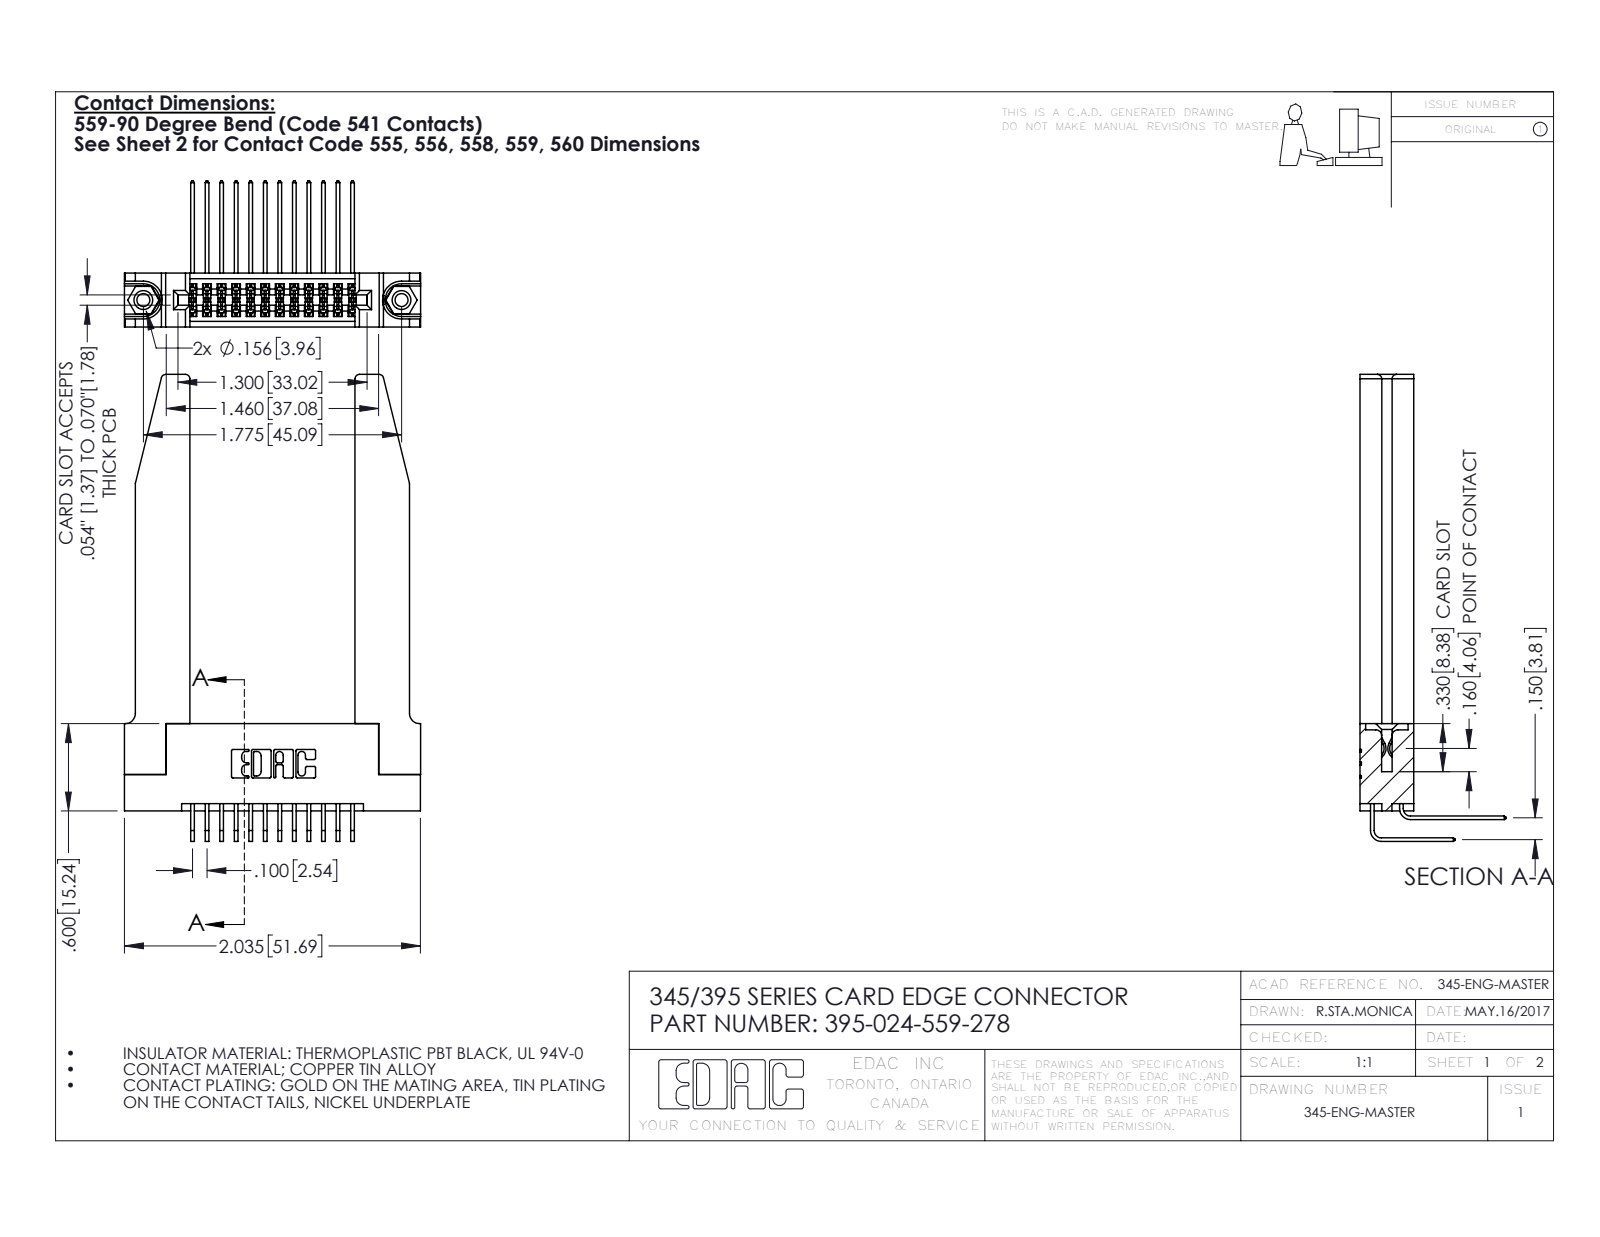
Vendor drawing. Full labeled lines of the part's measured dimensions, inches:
Part name (STEP PRODUCT): 345-292-001_558 559 Tail - 1; 395-024-559-278; 345-292-001_559 Tail - 2; 345-250-001_345-250-001-102 (+2 more)
STEP written by: SolidWorks 2016 (CONFIG_CONTROL_DESIGN)
Units: inches
Bodies: 29 solids, 1608 faces (1062 planar, 494 cylindrical, 52 other)
Overall size (bounding box): 3.209 × 2.036 × 1.005
Volume: 0.772 in³ · Surface area: 21.9 in²
Round holes (diameter × count): ⌀0.089 ×2, ⌀0.125 ×2, ⌀0.156 ×2, ⌀0.064 ×1
Round bosses / shafts (diameter × count): ⌀0.155 ×2
Partial cylindrical surfaces — rounded edges, fillets, slot ends (radius × count): R0.006 ×37, R0.01 ×22, R0.03 ×8, R0.007 ×6, R0.031 ×6, R0.026 ×3, R0.014 ×2, R0.019 ×2
Main face-to-face distances: 0.37, 0.072, 0.298, 0.2, 0.15, 0.148, 0.077, 0.22, 1.135, 0.098
Hole centre spacings: 0.27, 1.543, 1.775
